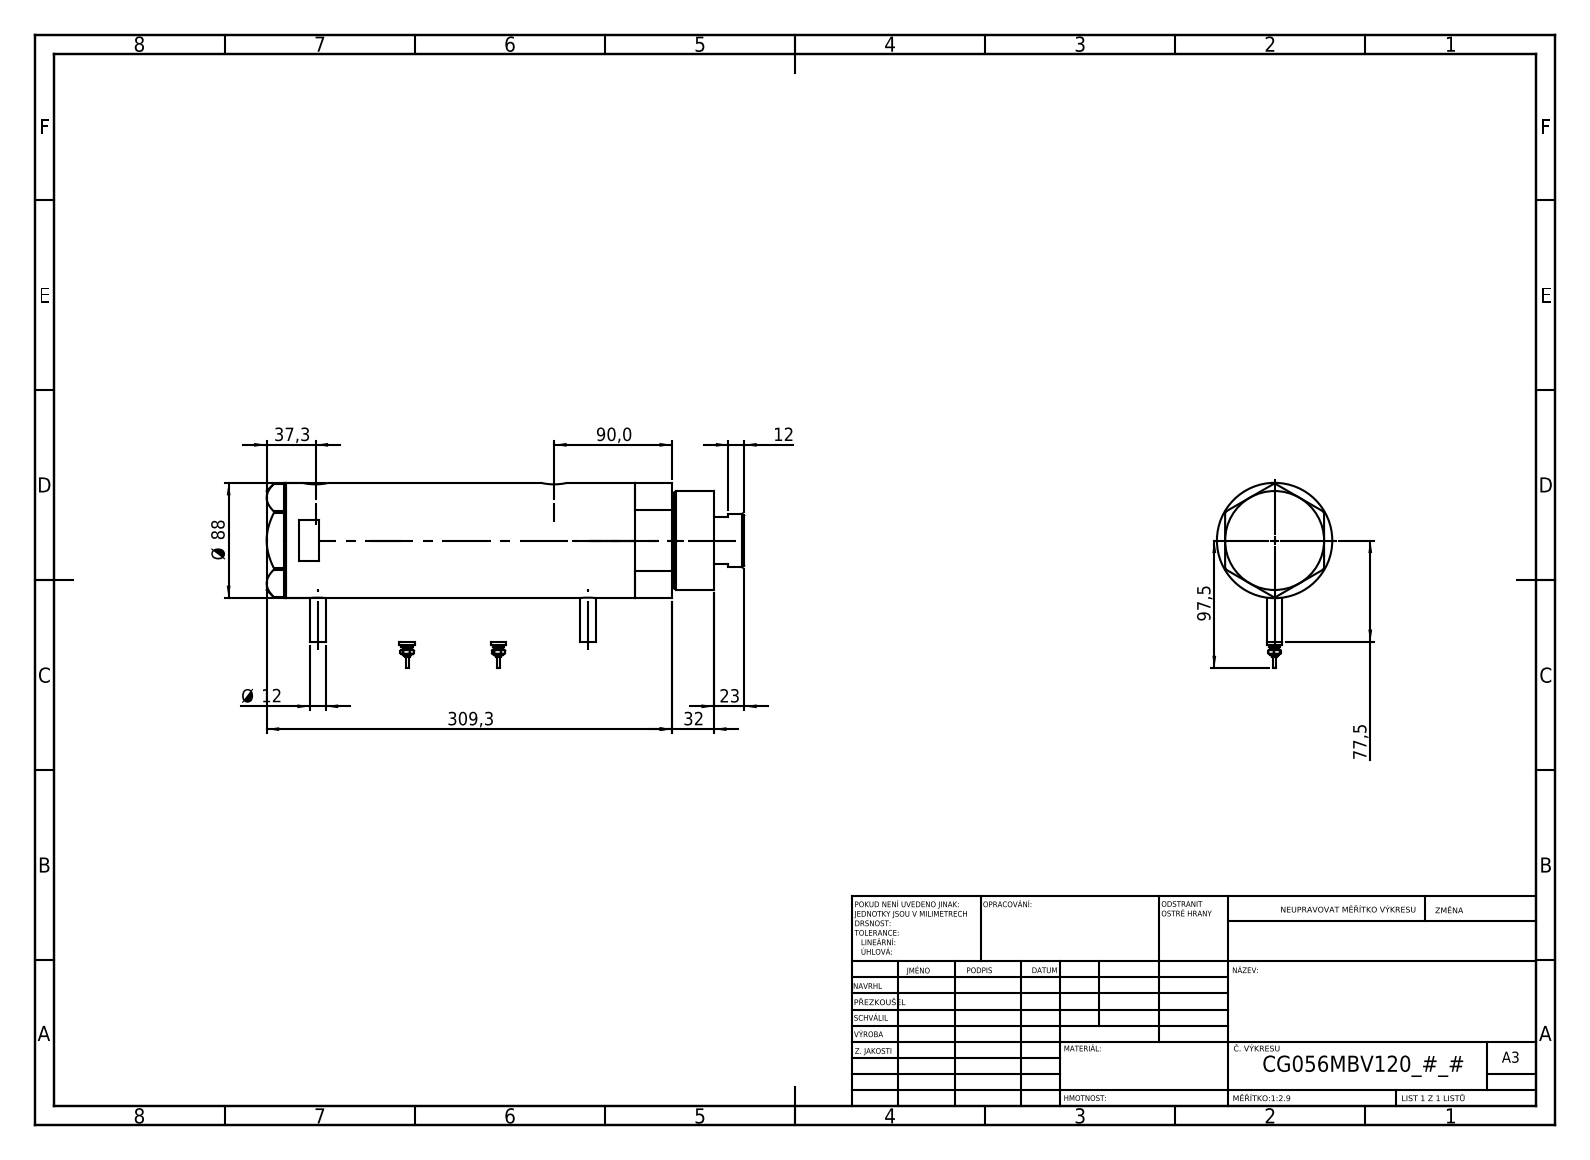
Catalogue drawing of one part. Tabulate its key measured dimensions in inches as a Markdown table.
| quantity | value |
| --- | --- |
| part name | V270CG_MIDDLE; V270CG_BACK; Switch; V270CG_VC (+1 more) |
| STEP written by | SolidWorks 2019 (CONFIG_CONTROL_DESIGN) |
| units | inches |
| bodies | 6 solids, 213 faces (80 planar, 69 cylindrical, 64 other) |
| overall size | 14.343 × 5.571 × 3.465 |
| volume | 115.4 in³ |
| surface area | 411.5 in² |
| round holes (diameter × count) | 0.492 × 2, 0.518 × 2, 0.787 × 2, 0.571 × 1, 1.654 × 1, 1.713 × 1, 2.205 × 1, 2.362 × 1, 3.15 × 1 |
| round bosses / shafts (diameter × count) | 0.472 × 4, 0.354 × 2, 0.276 × 2, 0.177 × 2, 0.098 × 2, 3.465 × 1, 2.953 × 1, 2.874 × 1 |
| main face-to-face distances | 8.047, 1.024, 7.024, 0.591, 1.614, 8.638, 12.846, 13.437, 11.823, 4.799 |
| hole center spacings | 0.067, 1.016, 7.098, 7.165, 8.114, 8.181 |
